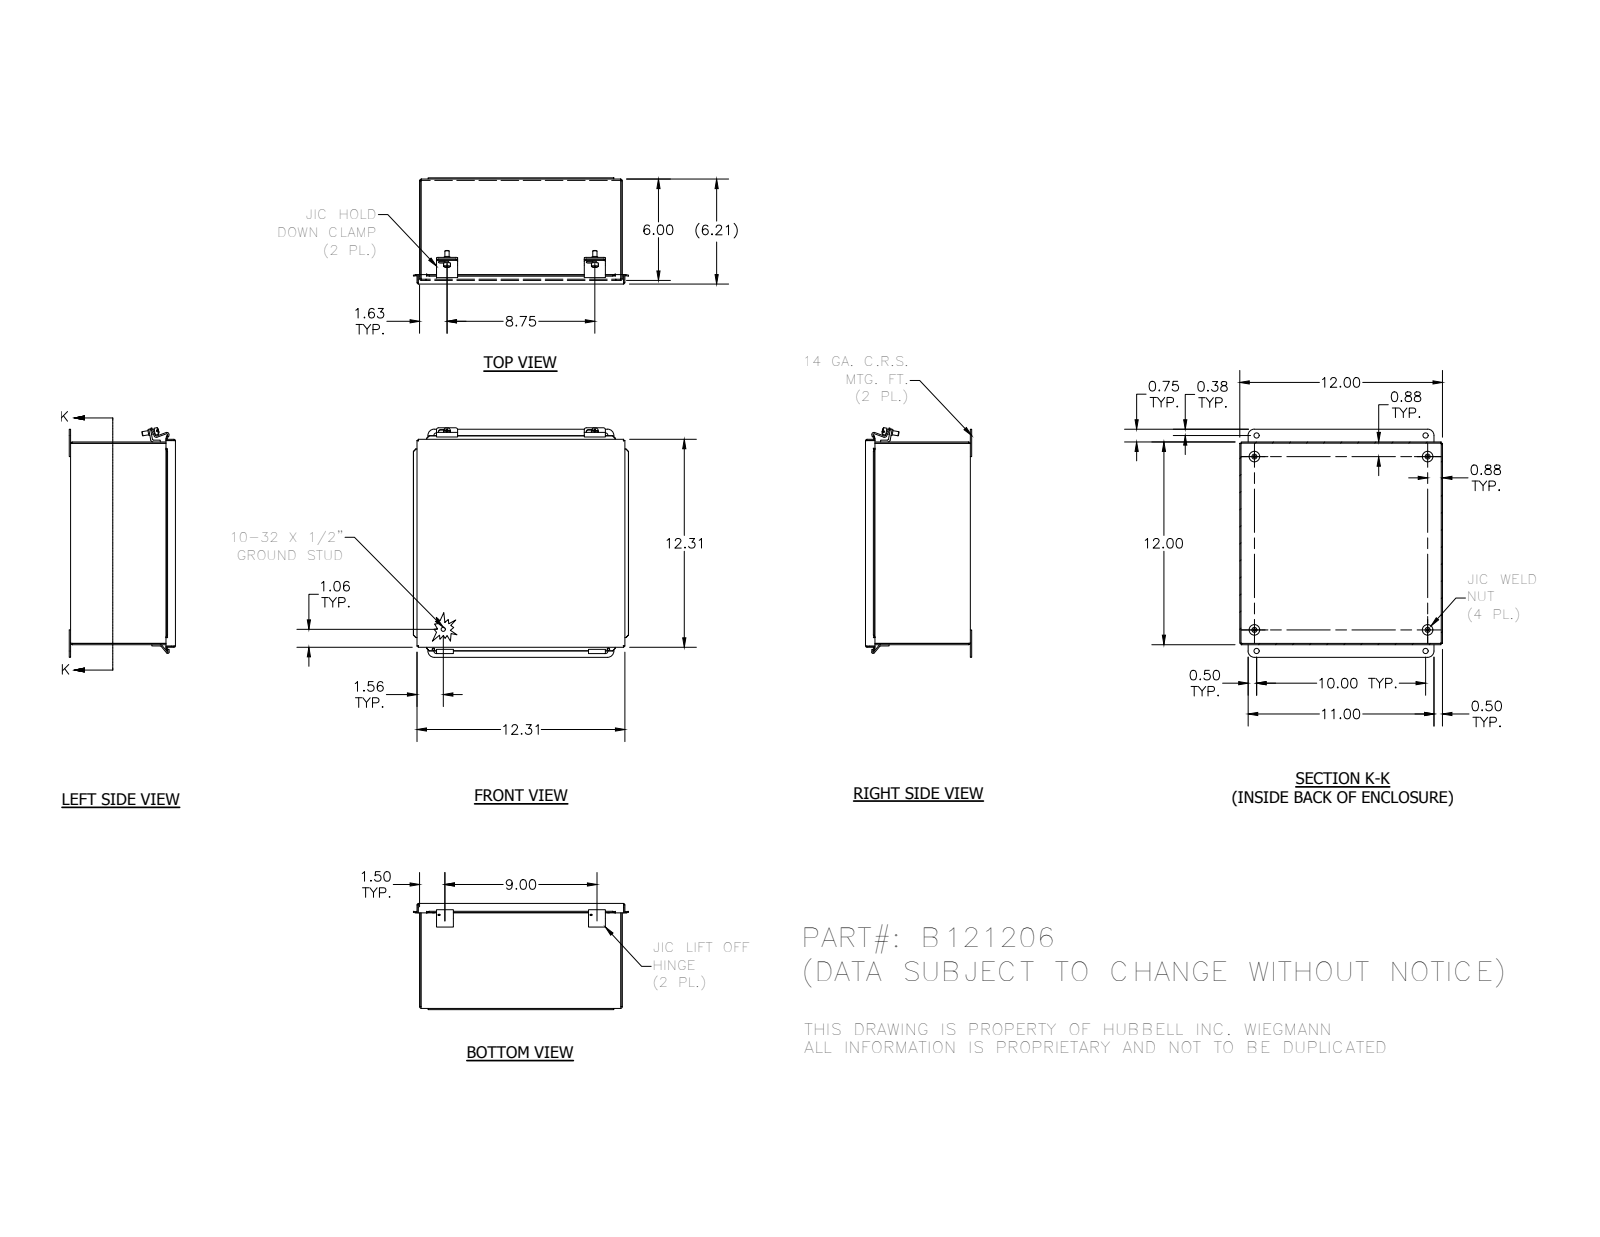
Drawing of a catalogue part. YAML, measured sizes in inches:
part_name: "B121206; 3499; 3485; C1001 (+7 more)"
step_written_by: "Autodesk Inventor 2012 (AUTOMOTIVE_DESIGN)"
units: inches
bodies: {solids: 19, faces: 422, planar: 279, cylindrical: 98, other: 45}
overall_size: [13.593, 12.739, 6.287]
volume: 52.79
surface_area: 1428
round_holes:
  - {diameter: 0.156, count: 4}
  - {diameter: 0.31, count: 4}
  - {diameter: 0.125, count: 2}
  - {diameter: 0.14, count: 2}
  - {diameter: 0.196, count: 2}
round_bosses_or_shafts:
  - {diameter: 0.625, count: 4}
  - {diameter: 0.3, count: 4}
  - {diameter: 0.25, count: 3}
  - {diameter: 0.41, count: 2}
  - {diameter: 0.344, count: 2}
  - {diameter: 0.19, count: 1}
partial_cylinders:
  - {radius: 0.031, count: 16}
  - {radius: 0.093, count: 8}
  - {radius: 0.105, count: 8}
  - {radius: 0.125, count: 8}
  - {radius: 0.133, count: 4}
  - {radius: 0.375, count: 4}
  - {radius: 0.063, count: 3}
  - {radius: 0.126, count: 3}
face_to_face_distances: [0.074, 11.926, 6.15, 0.062, 6.212, 6.076, 6.138, 12, 11.852, 0.075]
hole_center_spacings: [15.322, 1.257, 11.501, 10, 10.202, 10.202, 10.25, 10.25]
